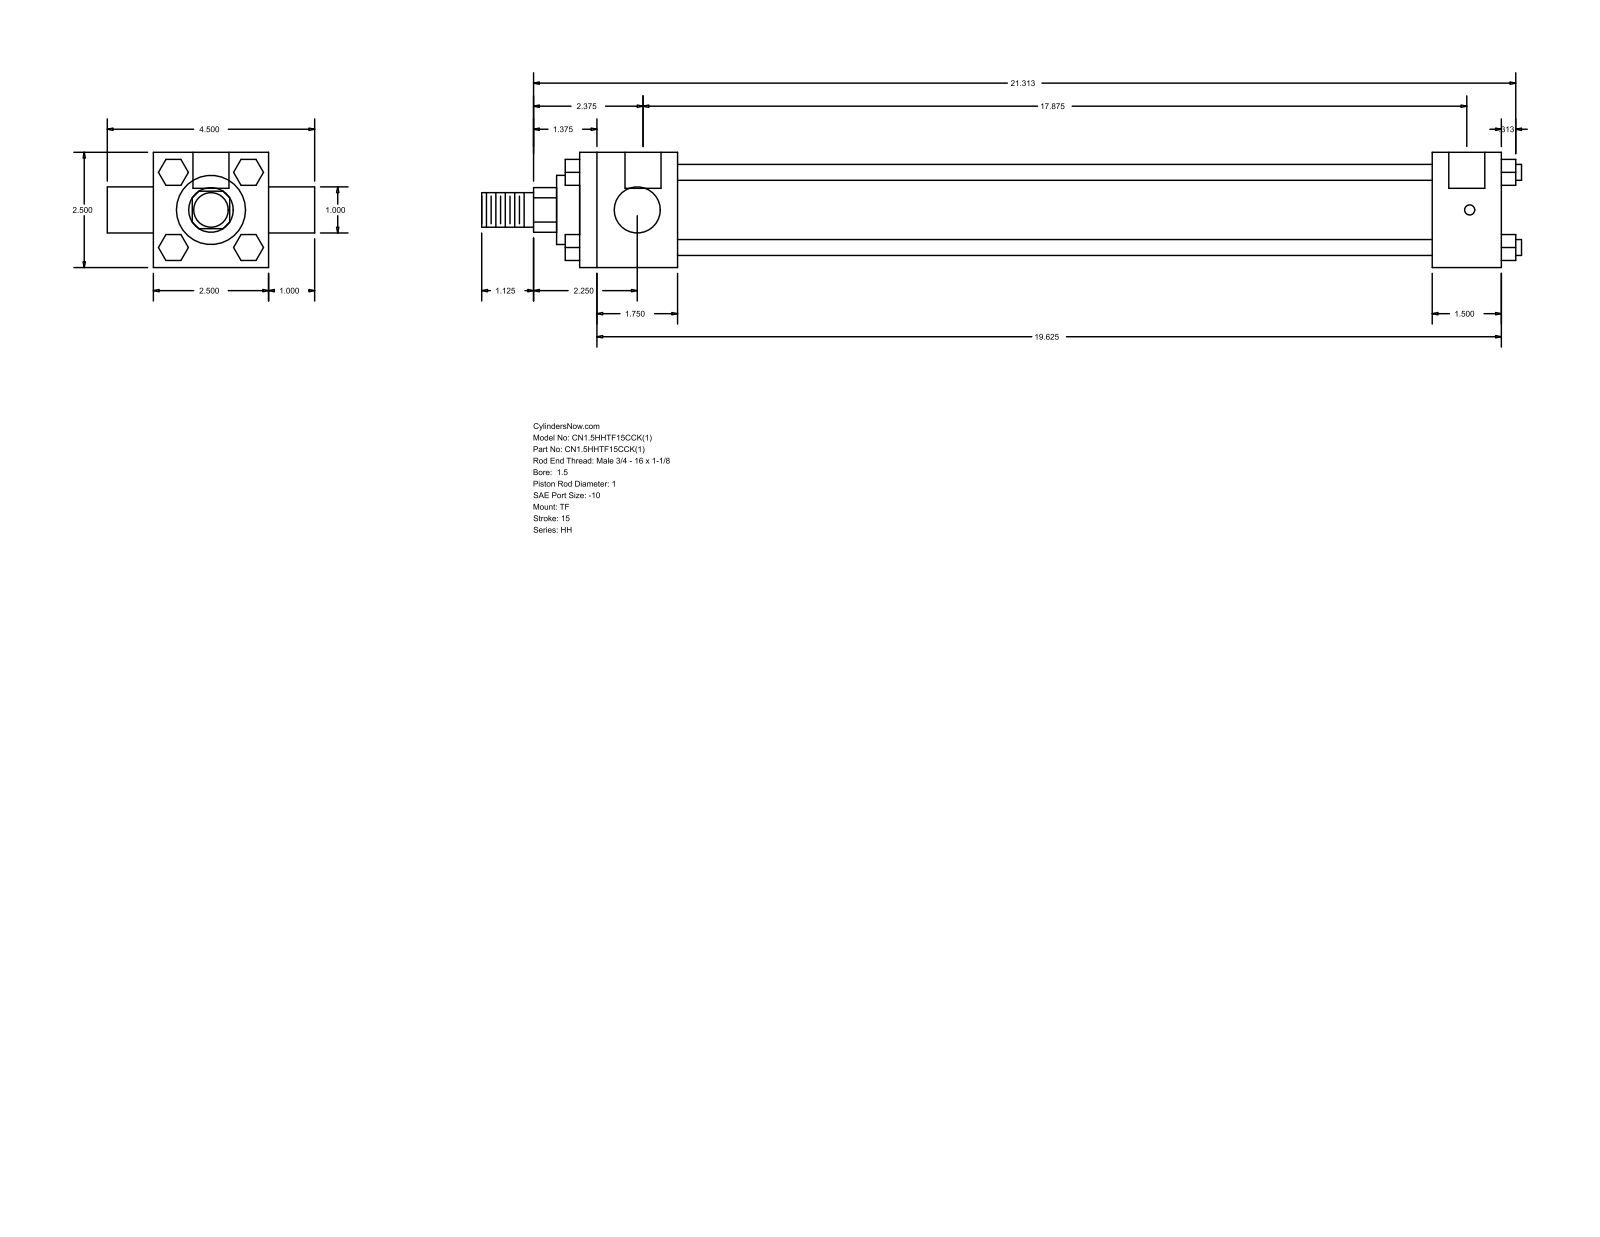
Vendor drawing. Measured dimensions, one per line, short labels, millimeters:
name: HH_TF__0150_1
written by: GSSL Pune (CONFIG_CONTROL_DESIGN)
unit: mm
bodies: 0 solids, 120 faces (92 planar, 28 cylindrical, 0 other)
size: 573.09 × 114.3 × 63.5
holes: 3× ⌀5.56, 2× ⌀19.84
bosses: 4× ⌀8.76, 2× ⌀25.4, 1× ⌀44.45, 1× ⌀38.1, 1× ⌀19.05
rounds: 1× R12.29
face distances: 63.5, 38.1, 454.02, 415.92, 53.98, 469.9, 508, 25.4, 20.7, 14.29
hole spacings: 1.59, 455.61, 454.02, 457.2
